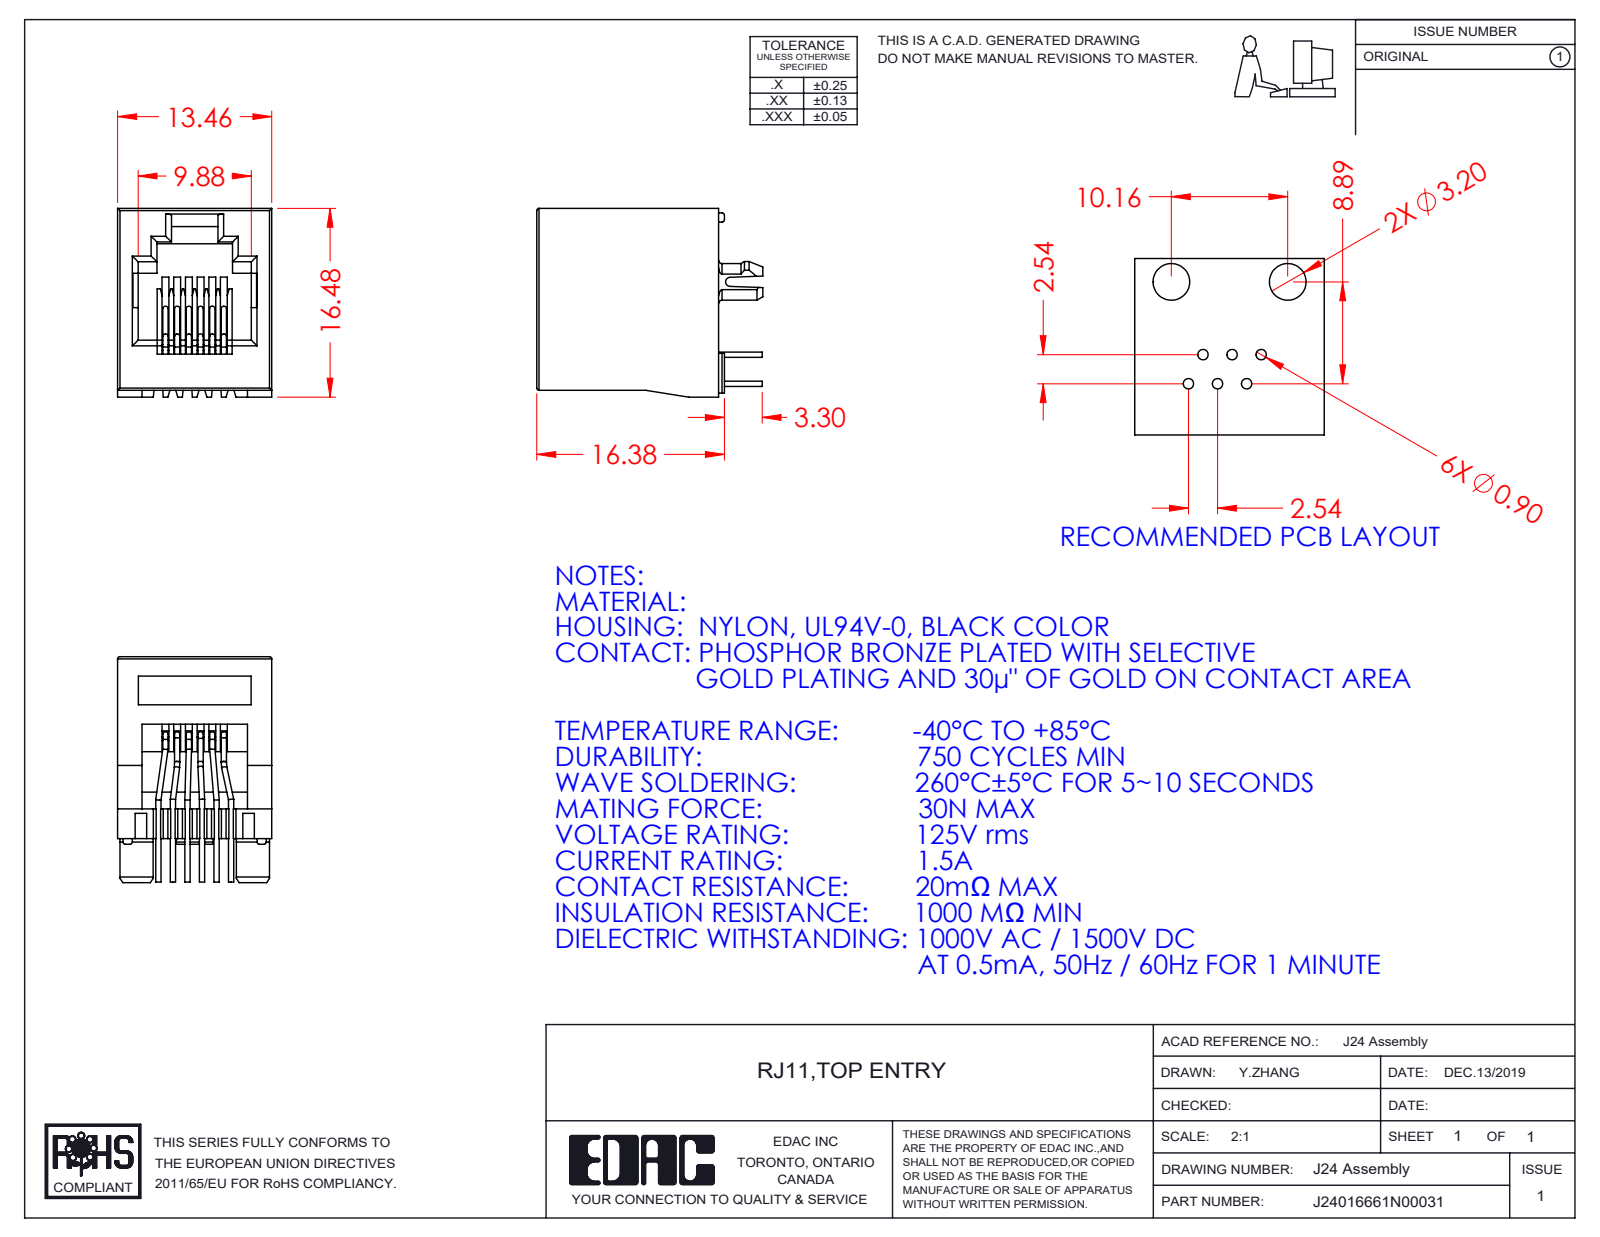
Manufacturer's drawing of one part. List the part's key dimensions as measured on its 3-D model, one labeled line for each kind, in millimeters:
Part name (STEP PRODUCT): 24 Insulator_Standard; RJ24016661N00031; 24 Contacts_Standard
STEP written by: SolidWorks 2016 (CONFIG_CONTROL_DESIGN)
Units: millimetres
Bodies: 7 solids, 444 faces (256 planar, 150 cylindrical, 38 other)
Overall size (bounding box): 19.73 × 16.48 × 13.46
Volume: 1 745 mm³ · Surface area: 2 930 mm²
Round holes (diameter × count): ⌀0.46 ×6, ⌀2.1 ×2
Round bosses / shafts (diameter × count): ⌀0.46 ×26
Partial cylindrical surfaces — rounded edges, fillets, slot ends (radius × count): R0.5 ×16, R0.2 ×10, R0.32 ×6, R0.34 ×6, R0.25 ×3, R1.6 ×2, R1.77 ×2, R0.4 ×1
Main face-to-face distances: 13.46, 1.02, 1.79, 11.67, 0.6, 15.87, 8.24, 3.43, 10.03, 1.64
Hole centre spacings: 2.84, 2.54, 4.58, 5.08, 13.1, 6.84, 10.16, 10.35
